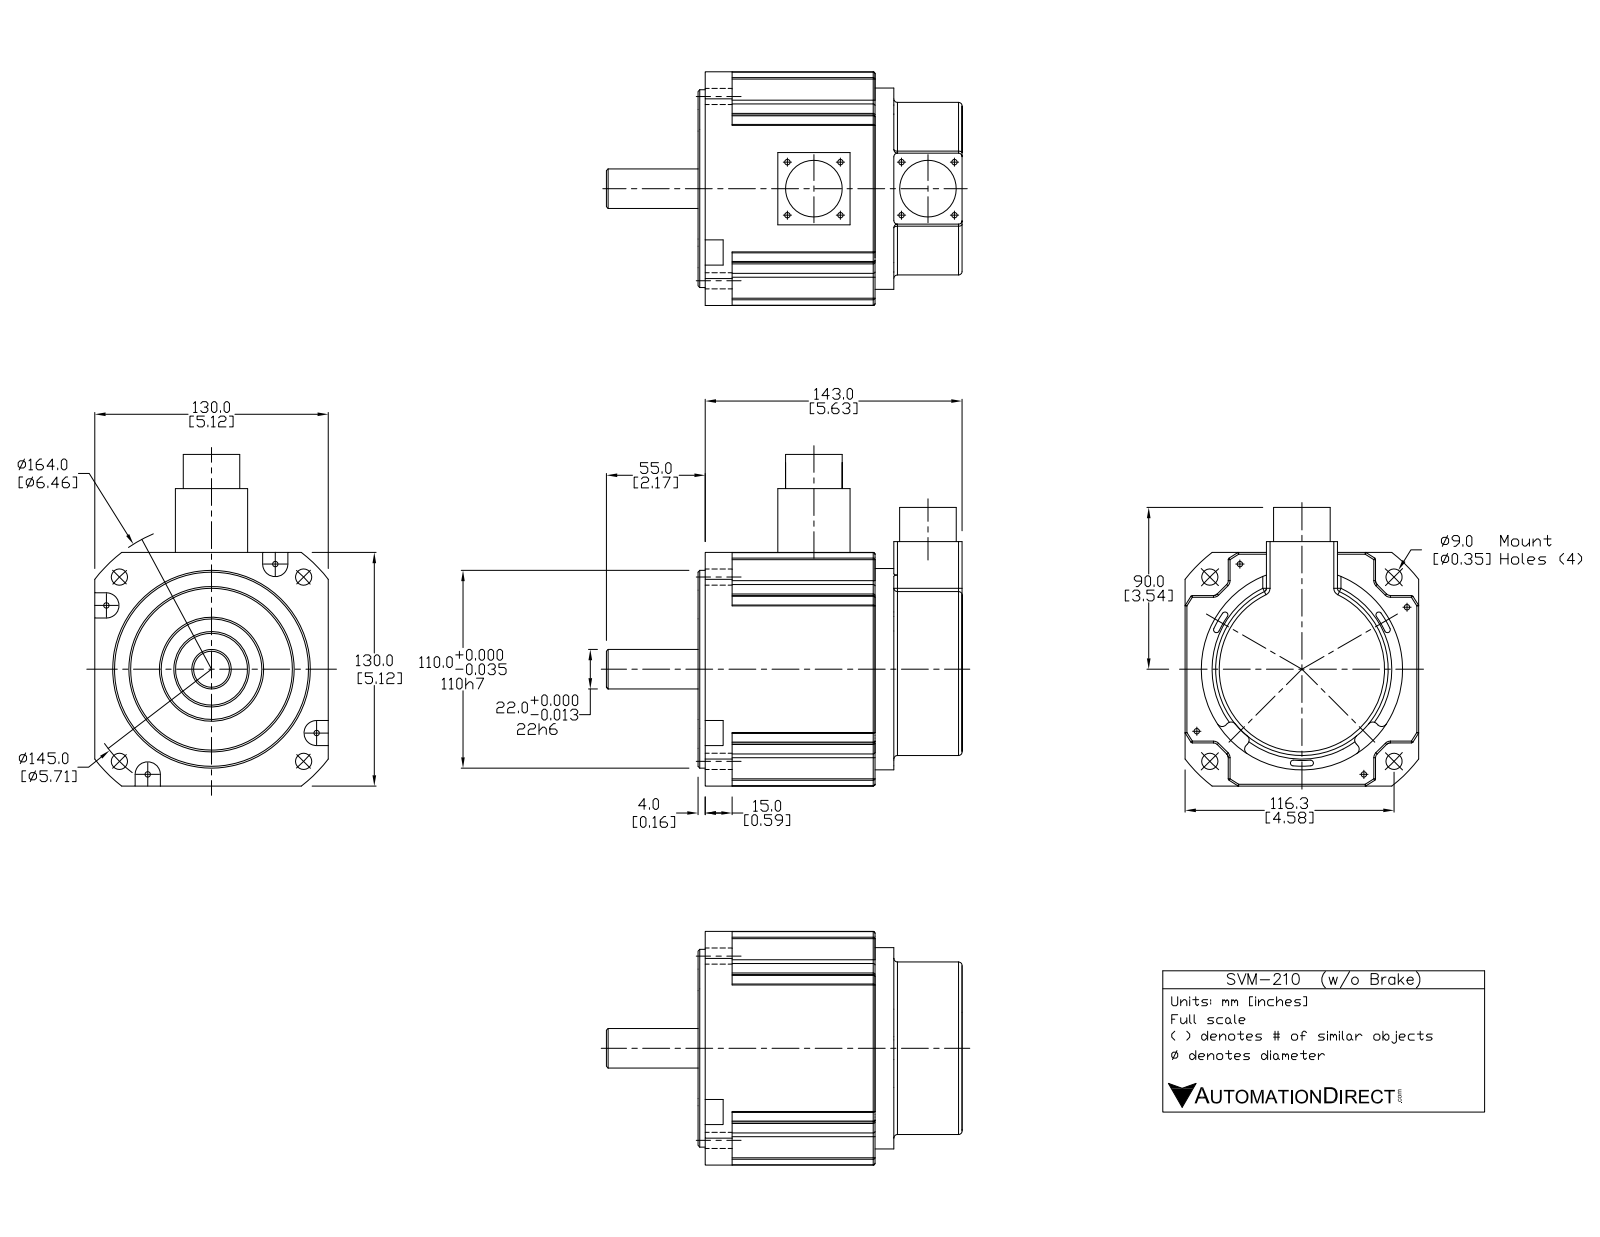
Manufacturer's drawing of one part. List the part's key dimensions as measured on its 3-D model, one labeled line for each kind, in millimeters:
Part name (STEP PRODUCT): SVM-210
STEP written by: SolidWorks 2015 (AUTOMOTIVE_DESIGN)
Units: millimetres
Bodies: 36 solids, 382 faces (187 planar, 114 cylindrical, 81 other)
Overall size (bounding box): 198 × 185.48 × 131.55
Volume: 1 907 000 mm³ · Surface area: 184 826 mm²
Round holes (diameter × count): ⌀9 ×4, ⌀27 ×1, ⌀27.2 ×1, ⌀90 ×1
Round bosses / shafts (diameter × count): ⌀2 ×17, ⌀1.5 ×6, ⌀12 ×4, ⌀10 ×4, ⌀2.5 ×3, ⌀31.5 ×2, ⌀112 ×1, ⌀110 ×1
Partial cylindrical surfaces — rounded edges, fillets, slot ends (radius × count): R2 ×4, R4 ×4, R7 ×4, R82 ×1
Main face-to-face distances: 70.5, 130, 24, 106, 85.5, 15, 57.5, 128, 143, 19
Hole centre spacings: 72.51, 102.54, 145.01, 64.53
